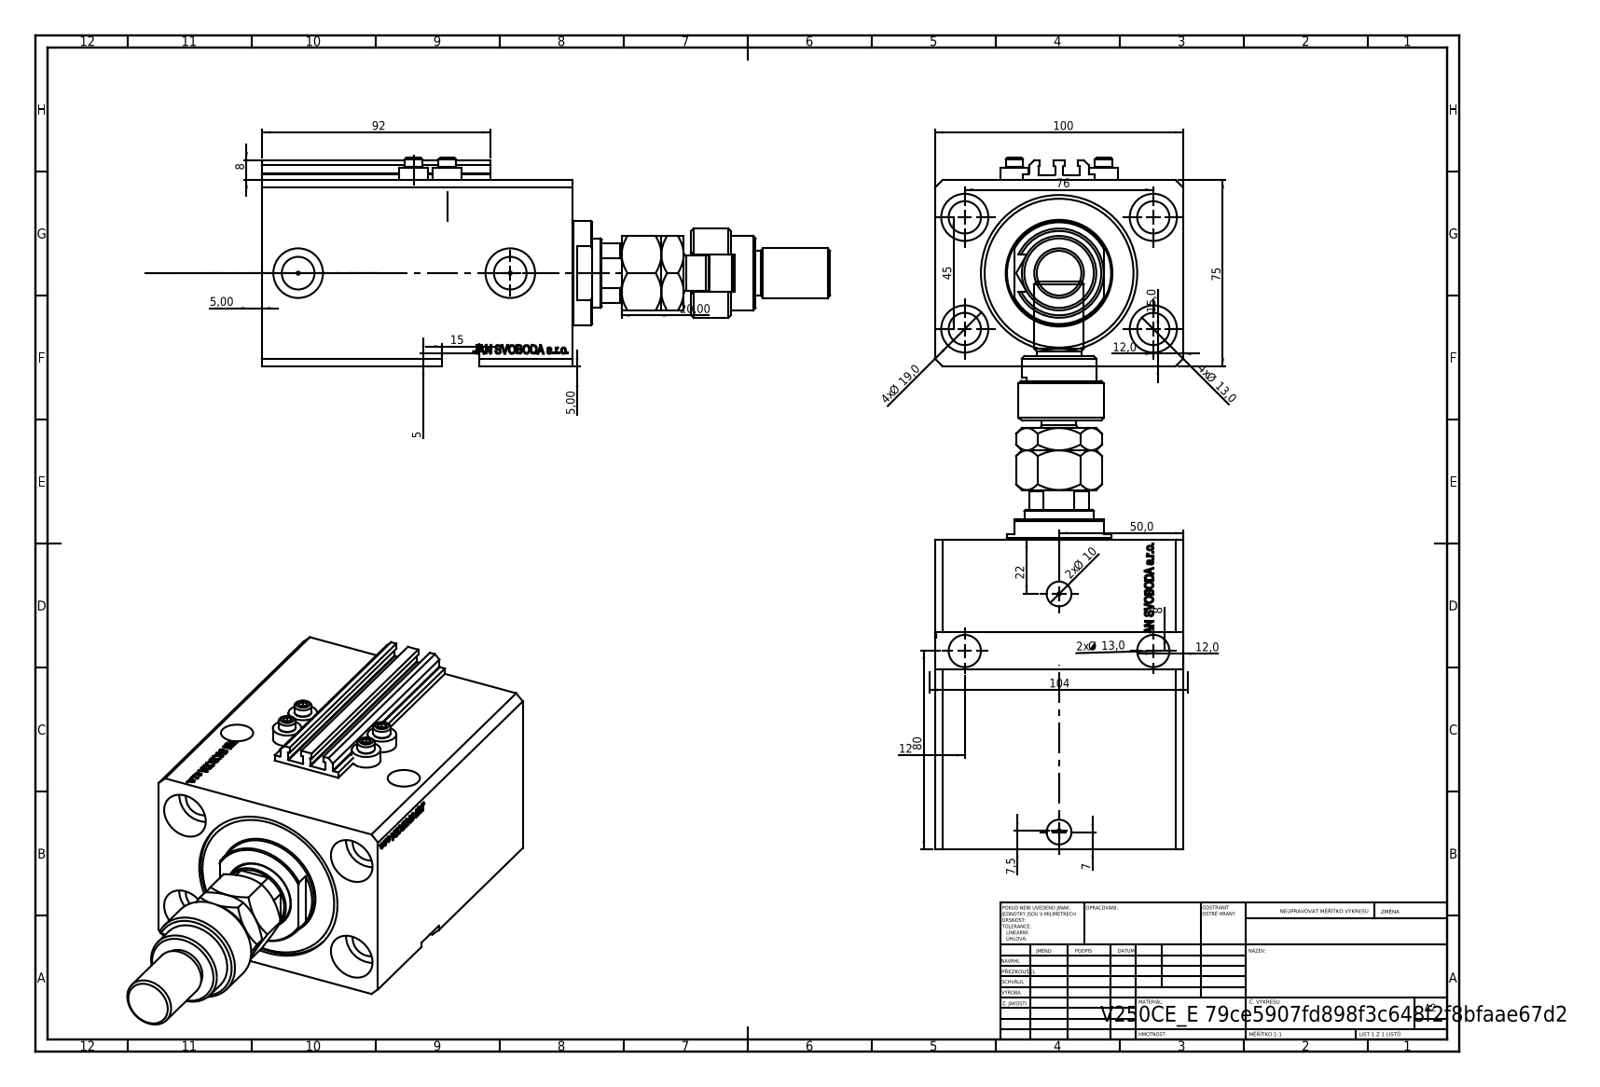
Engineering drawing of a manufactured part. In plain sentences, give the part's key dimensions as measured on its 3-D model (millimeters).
The part is named "ALLEN BOLT V250CE; MFA; V250CE_C_VCP; FEMALE_PART_FOR_DFA (+2 more)". Its 3-D file was written by "SolidWorks 2019 (CONFIG_CONTROL_DESIGN)". It is 10 solids with 1173 faces: 563 planar, 139 cylindrical and 471 other. Overall it measures 228.9 by 100 by 84 millimeters. Its volume is 831 736 cubic millimeters and its surface area 162 342 square millimeters. Round holes: 6 of diameter 13, 4 of diameter 1.25, 4 of diameter 4, 4 of diameter 19, 2 of diameter 10, 2 of diameter 13.16, 2 of diameter 20, 1 of diameter 18.5, 1 of diameter 28, 1 of diameter 50, 1 of diameter 63. Round bosses or shafts: 4 of diameter 11.6, 4 of diameter 7, 1 of diameter 42, 1 of diameter 36, 1 of diameter 30, 1 of diameter 22, 1 of diameter 20, 1 of diameter 18. Partial cylindrical surfaces (rounded edges, fillets, slot ends): 10 of radius 0.2, 1 of radius 7.5, 1 of radius 12, 1 of radius 13.5. The main face-to-face distances are 75, 100, 125, 11.9, 113.1, 98.4, 86.5, 26.6, 30, 48.4. The hole center spacings are 44.16, 76, 13.6, 20.72, 27.59, 33.62, 36, 38.48.
